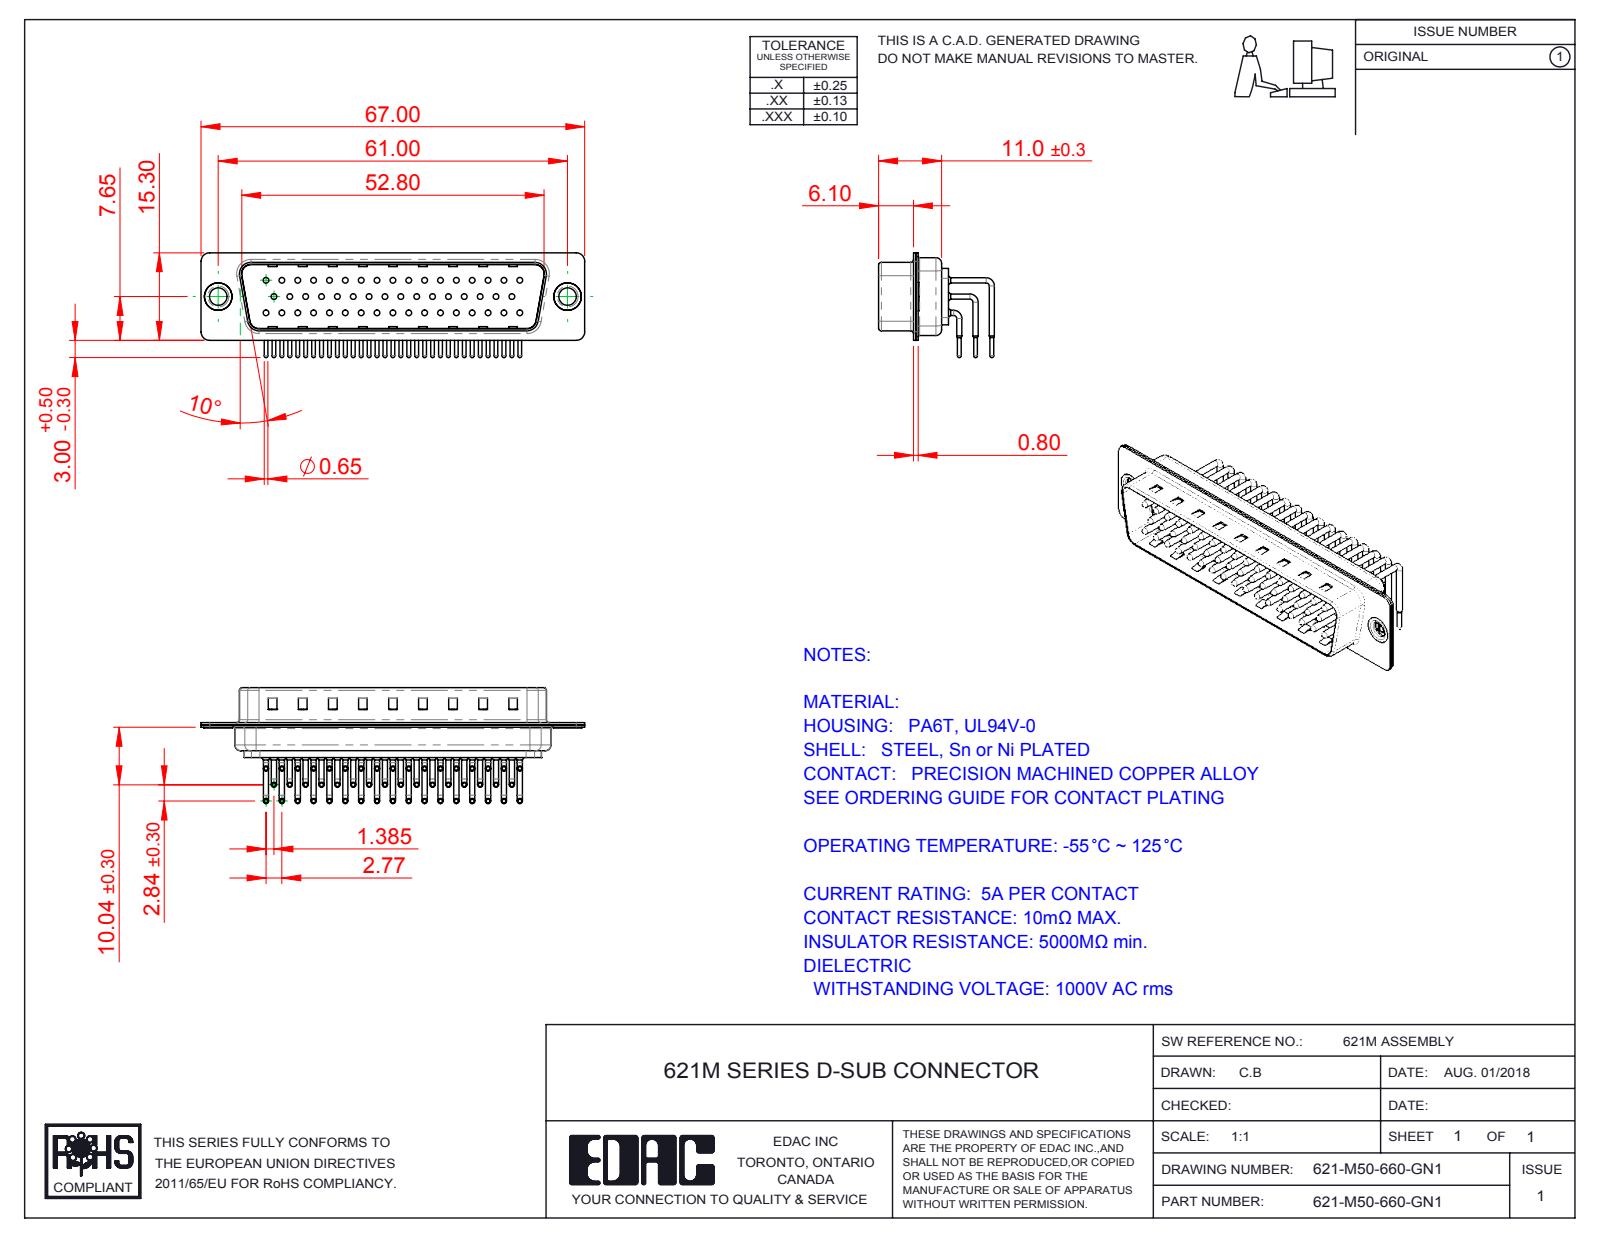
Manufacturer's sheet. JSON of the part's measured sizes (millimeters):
{"part_name": "621M Thru Hole Rivet; 621M Contact Row 1_50 Contacts; 621-M50-660-GN1; 621M Housing_50 Contacts (+4 more)", "step_written_by": "SolidWorks 2016 (CONFIG_CONTROL_DESIGN)", "units": "millimeters", "bodies": {"solids": 55, "faces": 5886, "planar": 3403, "cylindrical": 1925, "other": 558}, "overall_size": [67, 20.23, 18.3], "volume_mm3": 4843, "surface_area_mm2": 12425, "round_holes": [[1, 50], [1.7, 50], [2, 50], [3.05, 2], [4, 2], [4.8, 2]], "round_bosses_or_shafts": [[0.9, 100], [1.5, 50], [0.65, 50], [5, 2], [4.9, 2], [3.55, 2]], "partial_cylinders_radius": [[1.01, 50], [1.5, 16], [2, 12], [0.5, 8], [1.6, 8], [0.25, 4], [0.6, 4], [0.65, 4]], "face_to_face_distances": [0.4, 11.55, 5.7, 6.1, 12.38, 0.83, 0.82, 12.37, 13.2, 5.3], "hole_center_spacings": [2.77, 3.16, 5.54, 8.31, 11.08, 13.85, 16.62, 19.39]}
